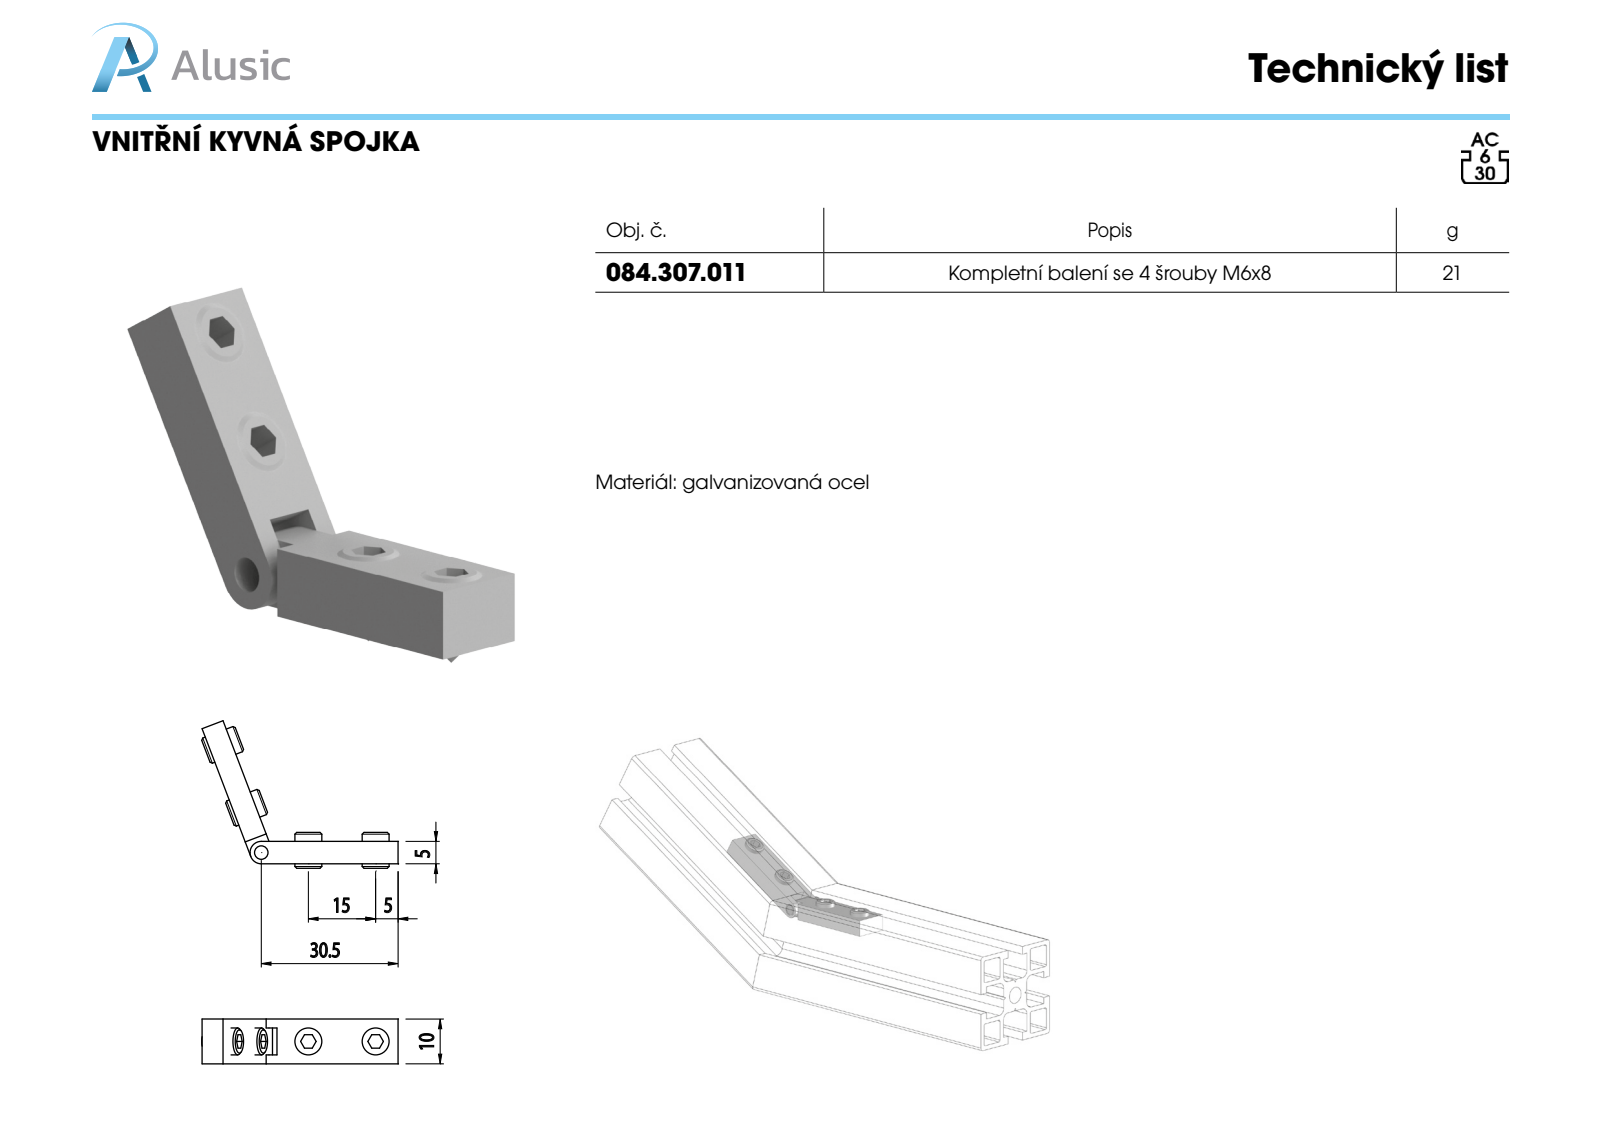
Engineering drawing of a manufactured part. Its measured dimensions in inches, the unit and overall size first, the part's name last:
Units: inches
Overall size (bounding box): 2.29 × 0.785 × 0.394
Round holes (diameter × count): ⌀0.197 ×4, ⌀0.118 ×1
Round bosses / shafts (diameter × count): ⌀0.236 ×4, ⌀0.197 ×1
Main face-to-face distances: 0.197, 0.394, 0.079, 0.315, 1.063, 0.256, 0.059, 0.236, 0.177, 0.118
Hole centre spacings: 0.591
Volume: 0.176 in³ · Surface area: 4.411 in²
Bodies: 6 solids, 93 faces (49 planar, 28 cylindrical, 16 other)
Part name (STEP PRODUCT): 084.307.011; socket set screw cone point_iso_ISO 4027 - M6 x 5-C; 084.307.011a; 084.307.011b
STEP written by: SolidWorks 2011 (CONFIG_CONTROL_DESIGN)
